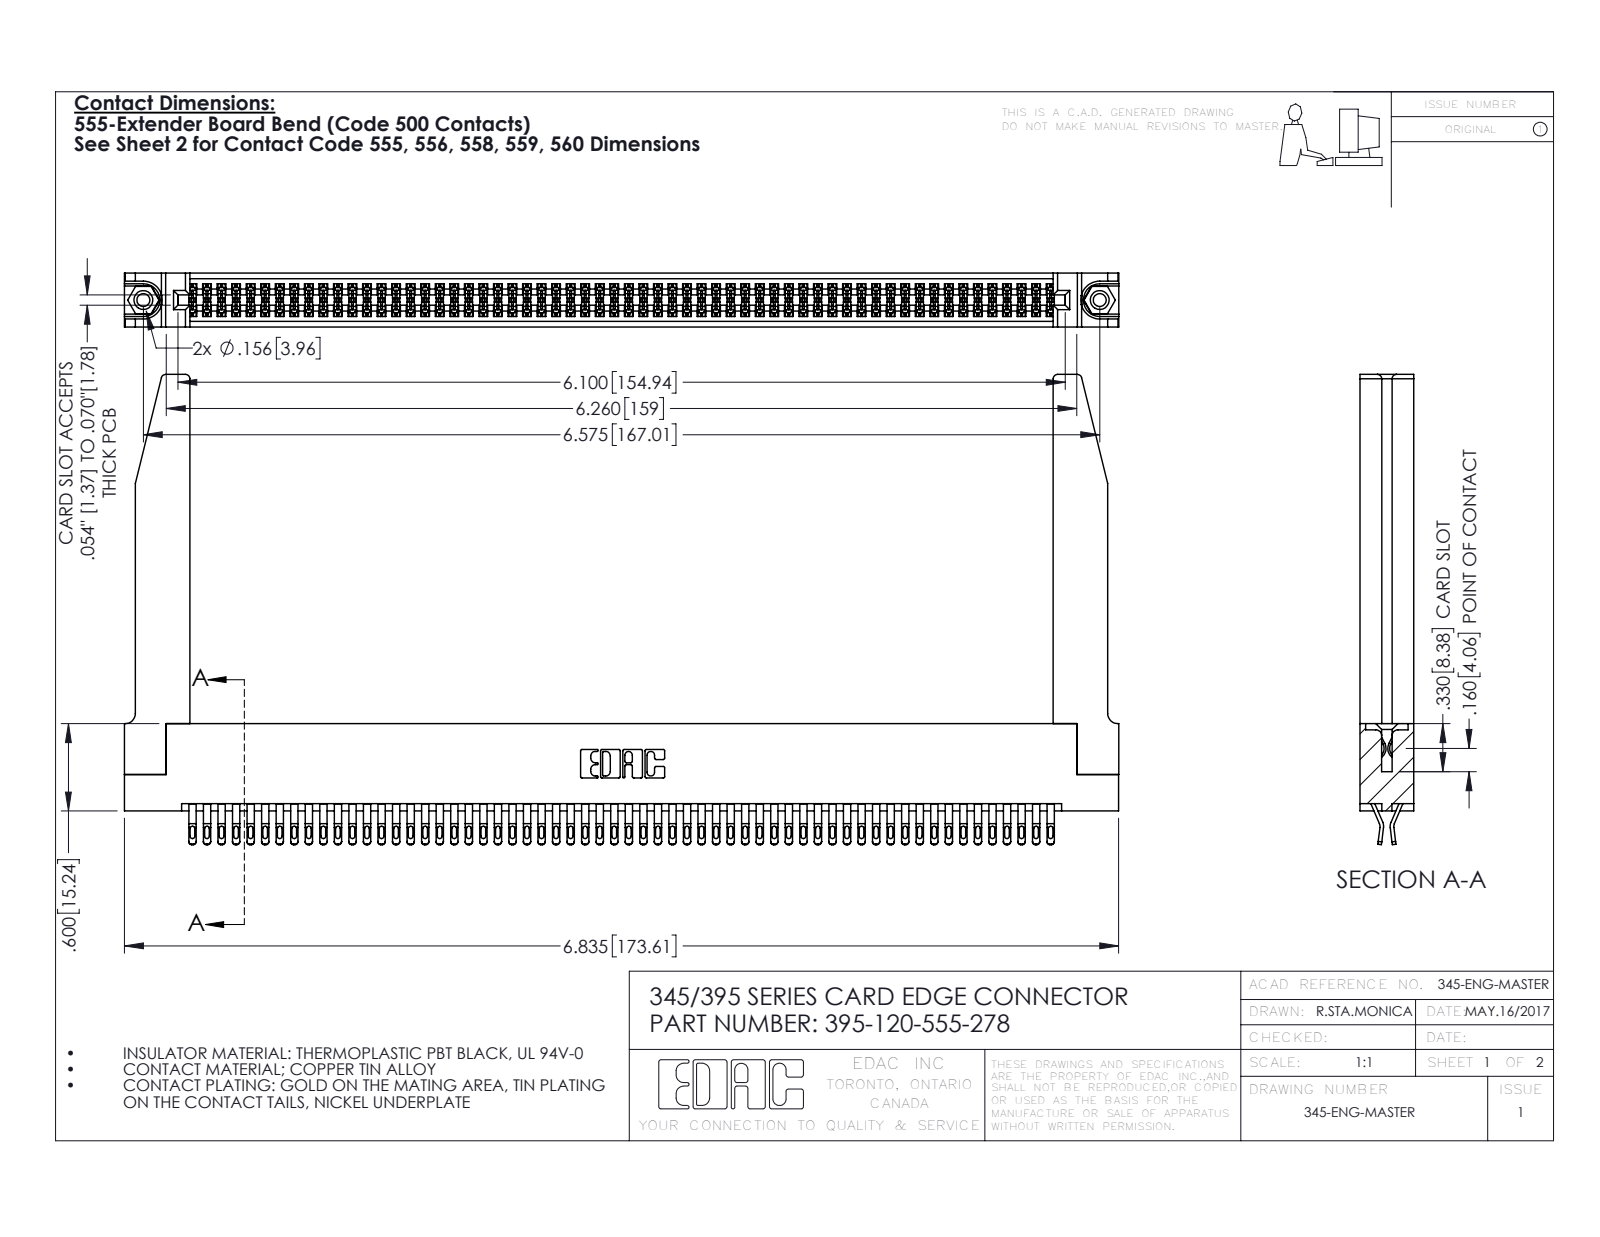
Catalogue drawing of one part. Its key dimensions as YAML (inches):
part_name: "345-220-078_345-220-078; 345 Part_Flush Mounting Lugs - 0.156 Dia-TH; 345-292-001_555 Tail; 395-120-555-278 (+1 more)"
step_written_by: "SolidWorks 2016 (CONFIG_CONTROL_DESIGN)"
units: inches
bodies: {solids: 125, faces: 7080, planar: 3942, cylindrical: 3086, other: 52}
overall_size: [6.836, 3.232, 0.37]
volume: 1.535
surface_area: 52.84
round_holes:
  - {diameter: 0.089, count: 2}
  - {diameter: 0.125, count: 2}
  - {diameter: 0.156, count: 2}
  - {diameter: 0.064, count: 1}
round_bosses_or_shafts:
  - {diameter: 0.155, count: 2}
partial_cylinders:
  - {radius: 0.016, count: 300}
  - {radius: 0.02, count: 240}
  - {radius: 0.006, count: 180}
  - {radius: 0.01, count: 22}
  - {radius: 0.03, count: 8}
  - {radius: 0.007, count: 6}
  - {radius: 0.031, count: 6}
  - {radius: 0.026, count: 3}
face_to_face_distances: [0.072, 0.37, 0.298, 0.025, 0.2, 0.098, 0.272, 0.225, 0.175, 0.148]
hole_center_spacings: [0.27, 6.339, 6.575]
